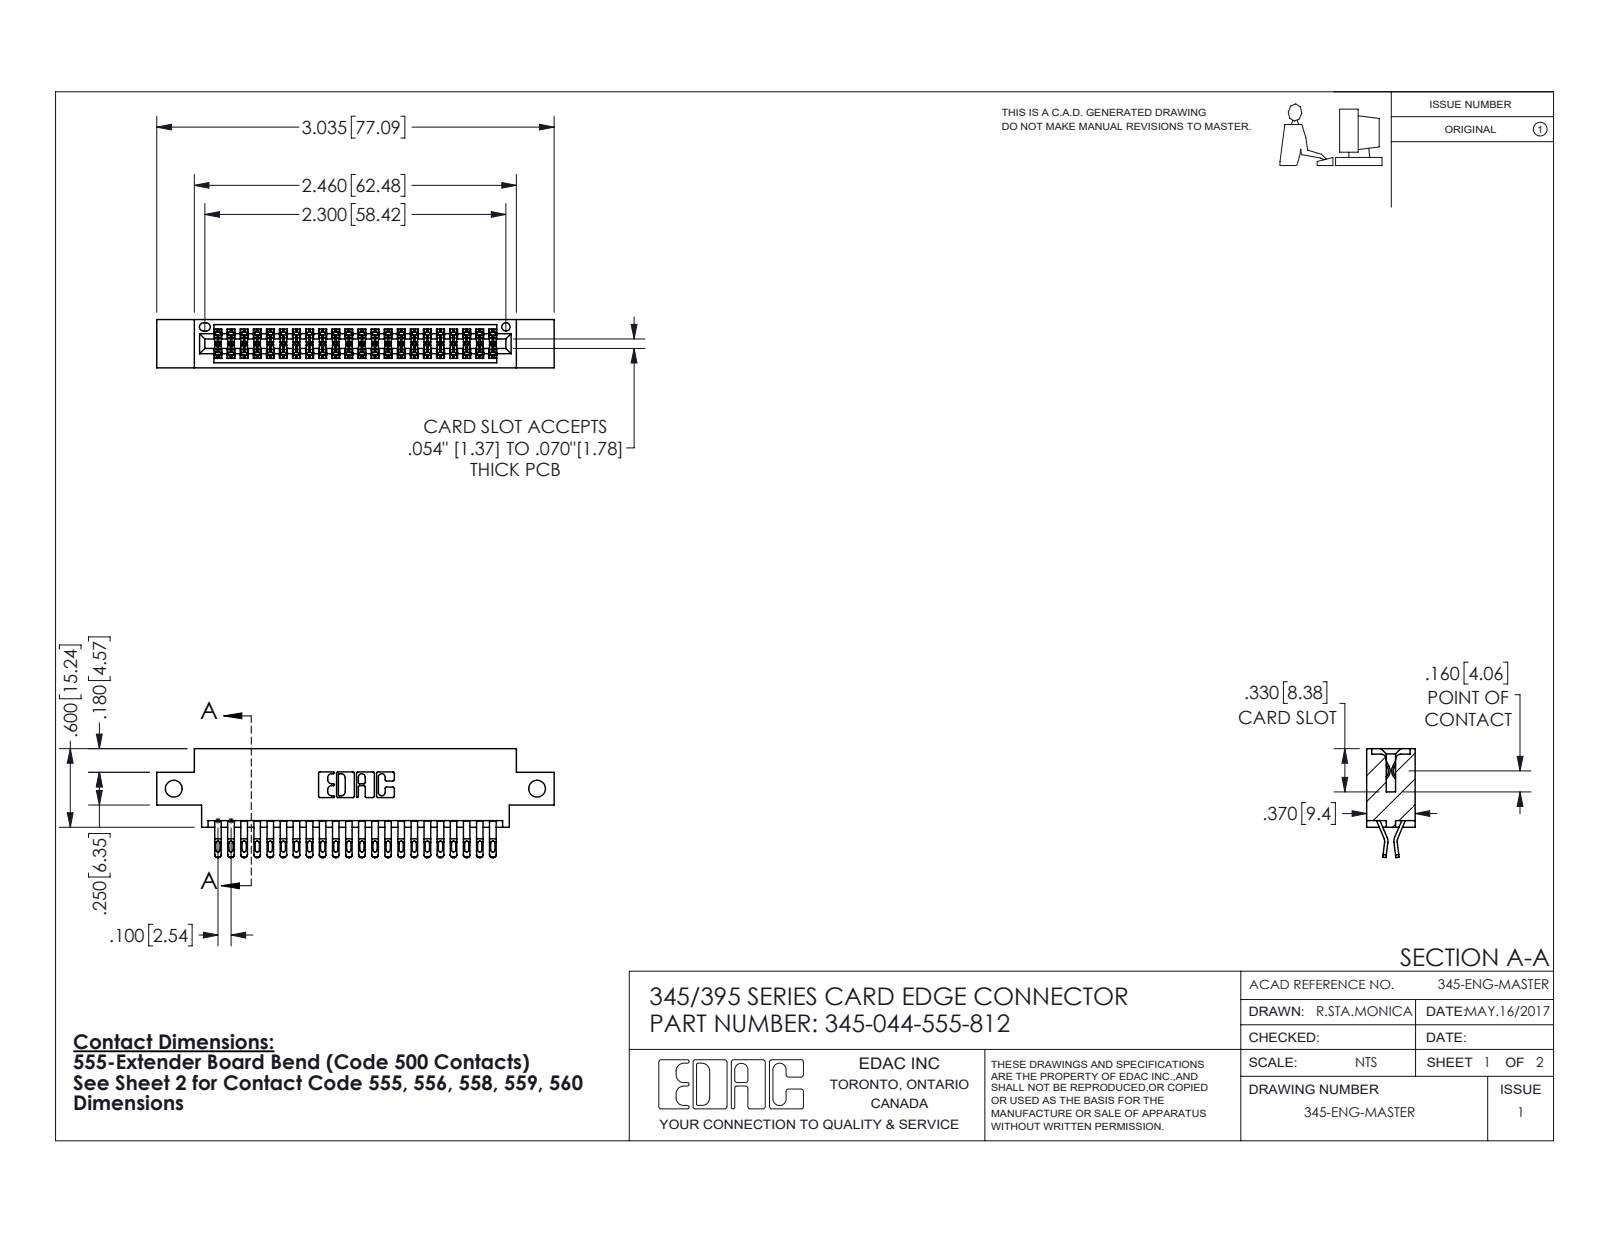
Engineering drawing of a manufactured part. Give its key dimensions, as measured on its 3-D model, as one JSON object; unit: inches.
{"part_name": "345-292-001_555 Tail; 345 Part_0.170 Offset - Side Mount; 345-044-555-812", "step_written_by": "SolidWorks 2016 (CONFIG_CONTROL_DESIGN)", "units": "inches", "bodies": {"solids": 45, "faces": 2594, "planar": 1448, "cylindrical": 1146, "other": 0}, "overall_size": [3.035, 0.832, 0.37], "volume_in3": 0.441, "surface_area_in2": 16.66, "round_holes": [[0.128, 2], [0.064, 1]], "partial_cylinders_radius": [[0.016, 110], [0.02, 88], [0.006, 66], [0.01, 22], [0.007, 6], [0.031, 6], [0.026, 3], [0.01, 2]], "face_to_face_distances": [0.298, 0.072, 0.37, 0.025, 0.2, 0.098, 0.272, 0.225, 0.175, 0.15], "hole_center_spacings": [2.775]}
